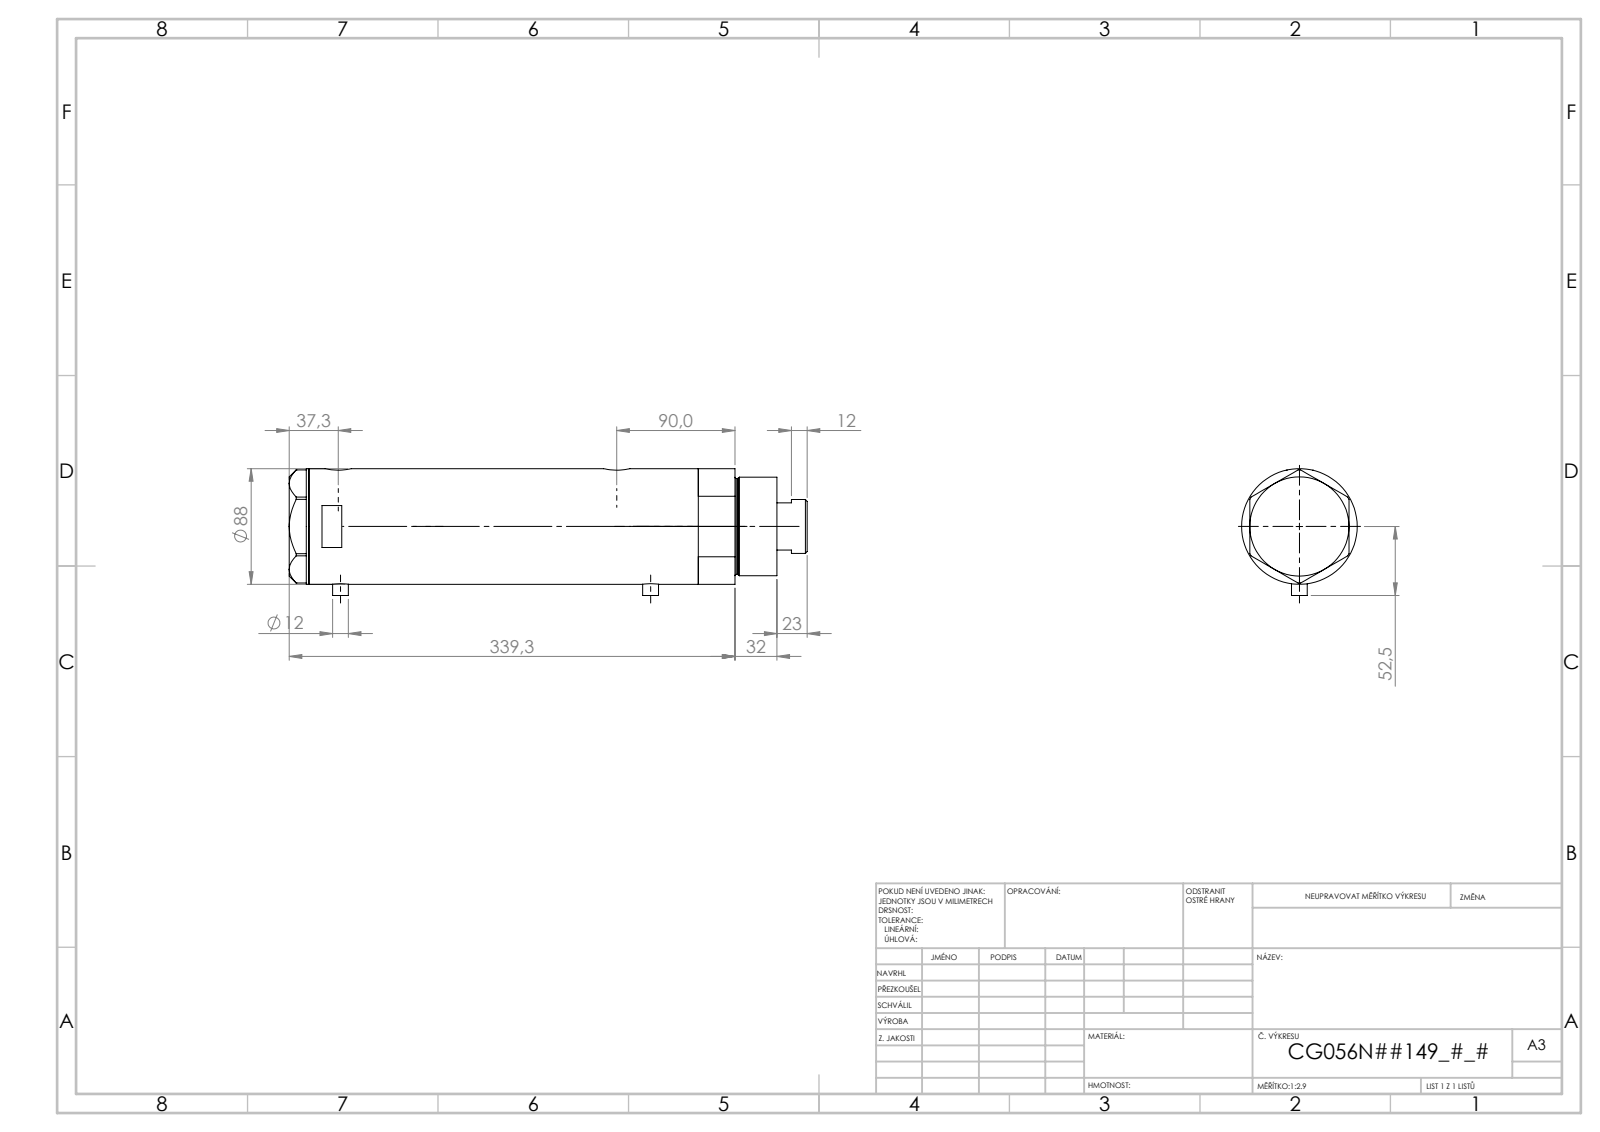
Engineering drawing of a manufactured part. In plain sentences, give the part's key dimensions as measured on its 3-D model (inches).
The part is named "V270CG_FRONT; V270CG_VC; V270CG_MIDDLE; V270CG_BACK". Its 3-D file was written by "SolidWorks 2019 (CONFIG_CONTROL_DESIGN)". It is 4 solids with 121 faces: 52 planar, 49 cylindrical and 20 other. Overall it measures 15.524 by 3.799 by 3.465 inches. Its volume is 124.2 cubic inches and its surface area 433.9 square inches. Round holes: 2 of diameter 0.492, 2 of diameter 0.518, 2 of diameter 0.787, 1 of diameter 0.571, 1 of diameter 1.654, 1 of diameter 1.713, 1 of diameter 2.205, 1 of diameter 2.362, 1 of diameter 3.15. Round bosses or shafts: 2 of diameter 0.472, 1 of diameter 3.465, 1 of diameter 2.953, 1 of diameter 2.874, 1 of diameter 1.614. The main face-to-face distances are 9.228, 1.024, 8.205, 0.591, 1.614, 9.819, 14.028, 14.618, 13.004, 4.799. The hole center spacings are 0.067, 1.016, 8.28, 8.346, 9.295, 9.362.
